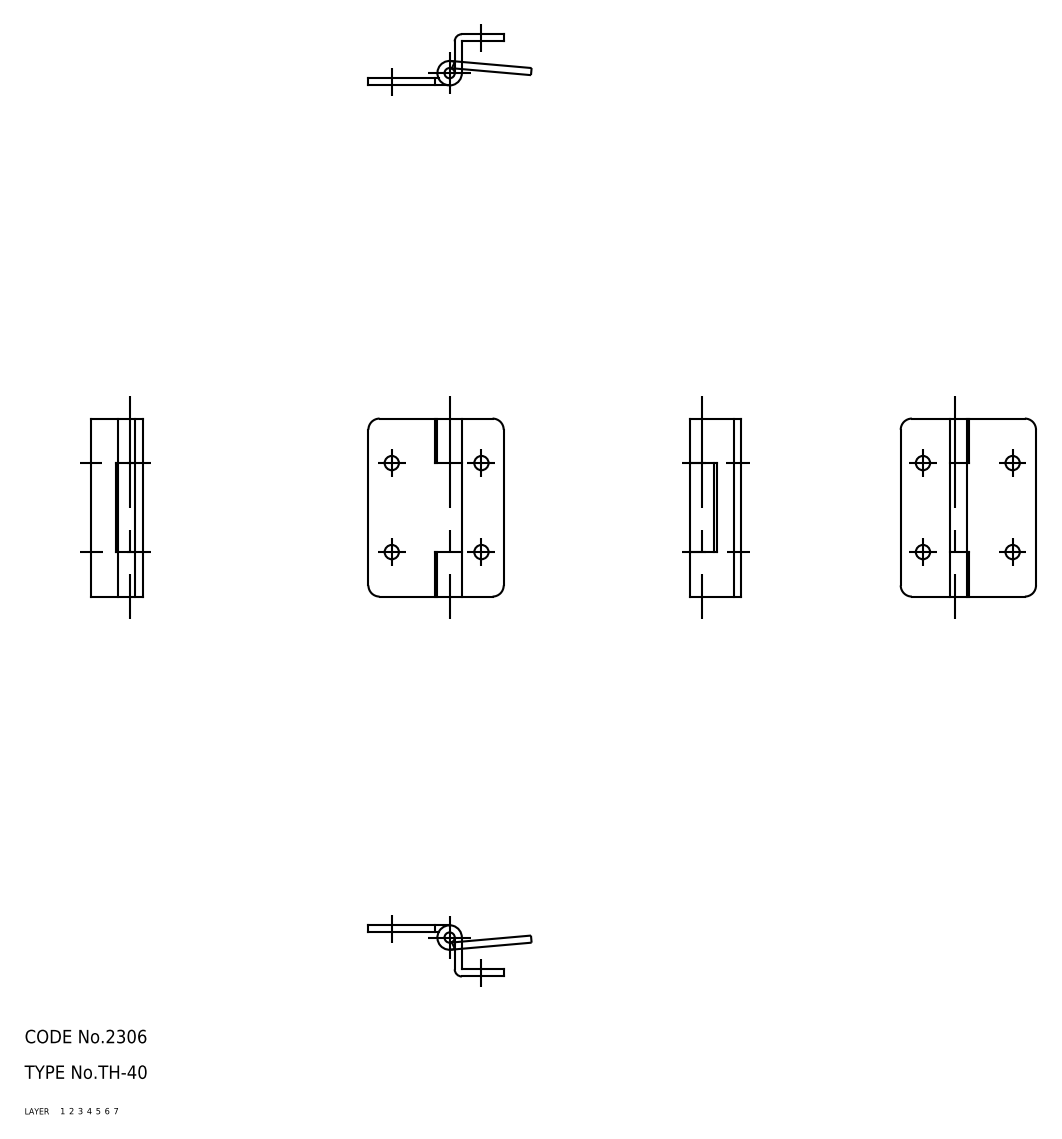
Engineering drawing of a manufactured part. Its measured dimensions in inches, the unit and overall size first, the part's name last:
Units: inches
Overall size (bounding box): 1.575 × 1.197 × 0.453
Volume: 0.174 in³ · Surface area: 6.482 in²
Bodies: 3 solids, 45 faces (0 planar, 0 cylindrical, 45 other)
Part name (STEP PRODUCT): shaft; hinge piece_B; hinge piece_A; TH_40_8768_36
STEP written by: CADfix (AUTOMOTIVE_DESIGN)
